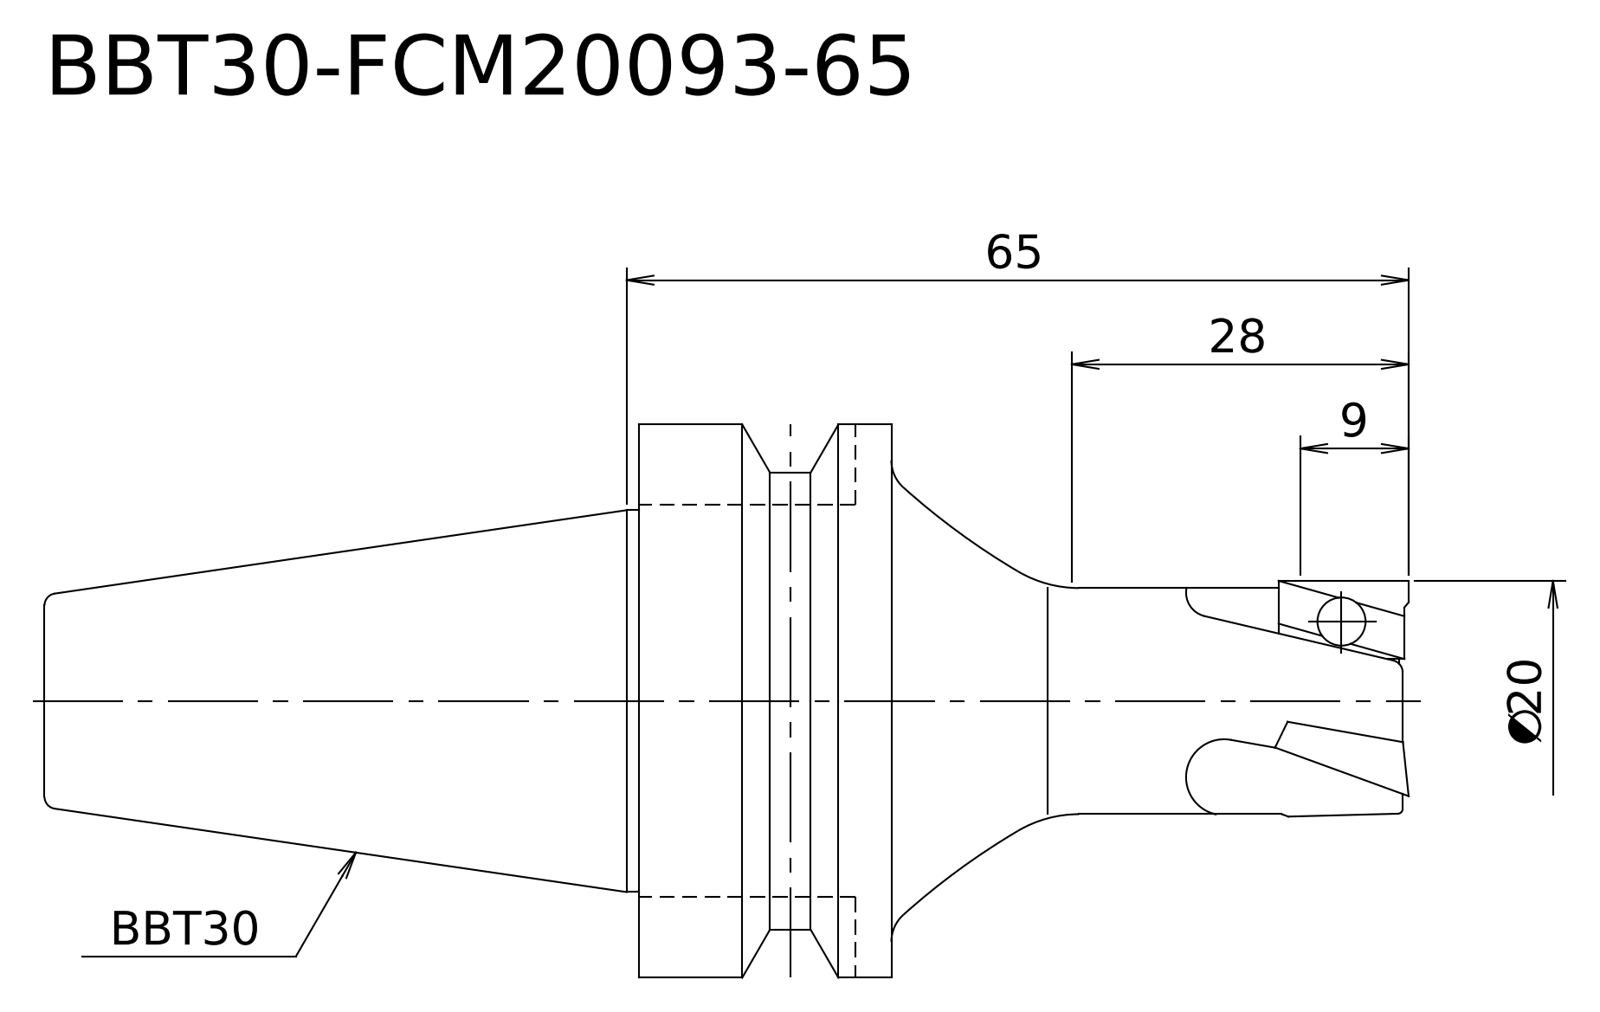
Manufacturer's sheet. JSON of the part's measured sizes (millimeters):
{"step_written_by": "Kubotek KeyCreator V8.5.1 (14335) (CONFIG_CONTROL_DESIGN)", "units": "millimeters", "bodies": {"solids": 1, "faces": 17, "planar": 4, "cylindrical": 6, "other": 7}, "overall_size": [113.4, 46, 46], "volume_mm3": 73182, "surface_area_mm2": 12564, "round_bosses_or_shafts": [[46, 1], [38, 1], [31.75, 1], [20, 1], [18.8, 1]], "face_to_face_distances": [21, 43, 64, 113.4, 70.4, 49.4]}
